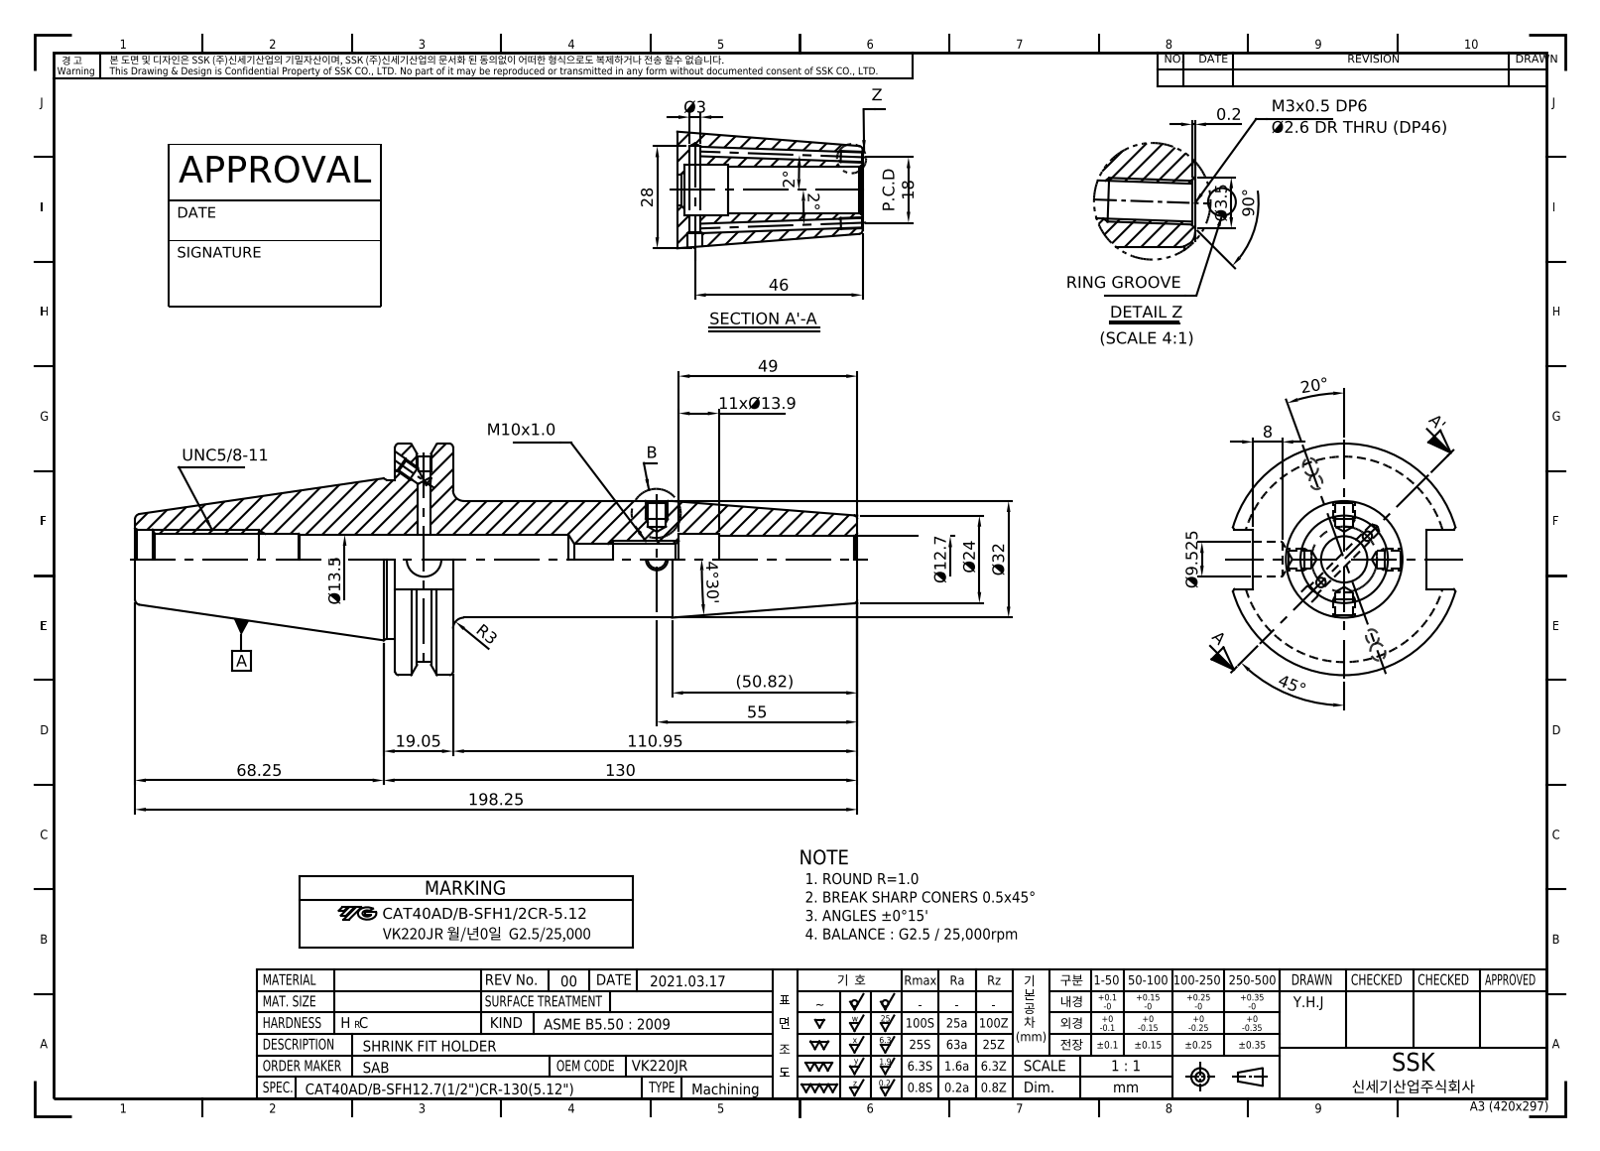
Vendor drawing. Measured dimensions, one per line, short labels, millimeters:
name: LO-CAT40ADB-SFH12.7CR-130
written by: Autodesk Inventor 2022 (AUTOMOTIVE_DESIGN)
unit: mm
bodies: 1 solid, 91 faces (37 planar, 31 cylindrical, 23 other)
size: 198.25 × 63.5 × 61.09
volume: 167 740 mm³; area: 35 686 mm²
holes: 4× ⌀3.24, 2× ⌀2.46, 2× ⌀4, 2× ⌀4.2, 1× ⌀8.92, 1× ⌀9.53, 1× ⌀12.7, 1× ⌀13, 1× ⌀13.39, 1× ⌀13.9, 1× ⌀16.3
bosses: 1× ⌀63.5, 1× ⌀43.6, 1× ⌀32
rounds: 1× R28.15
face distances: 15.88, 126.83, 110.95, 47.6, 16.38, 71.42, 87.3, 198.25, 77.47, 6.05
